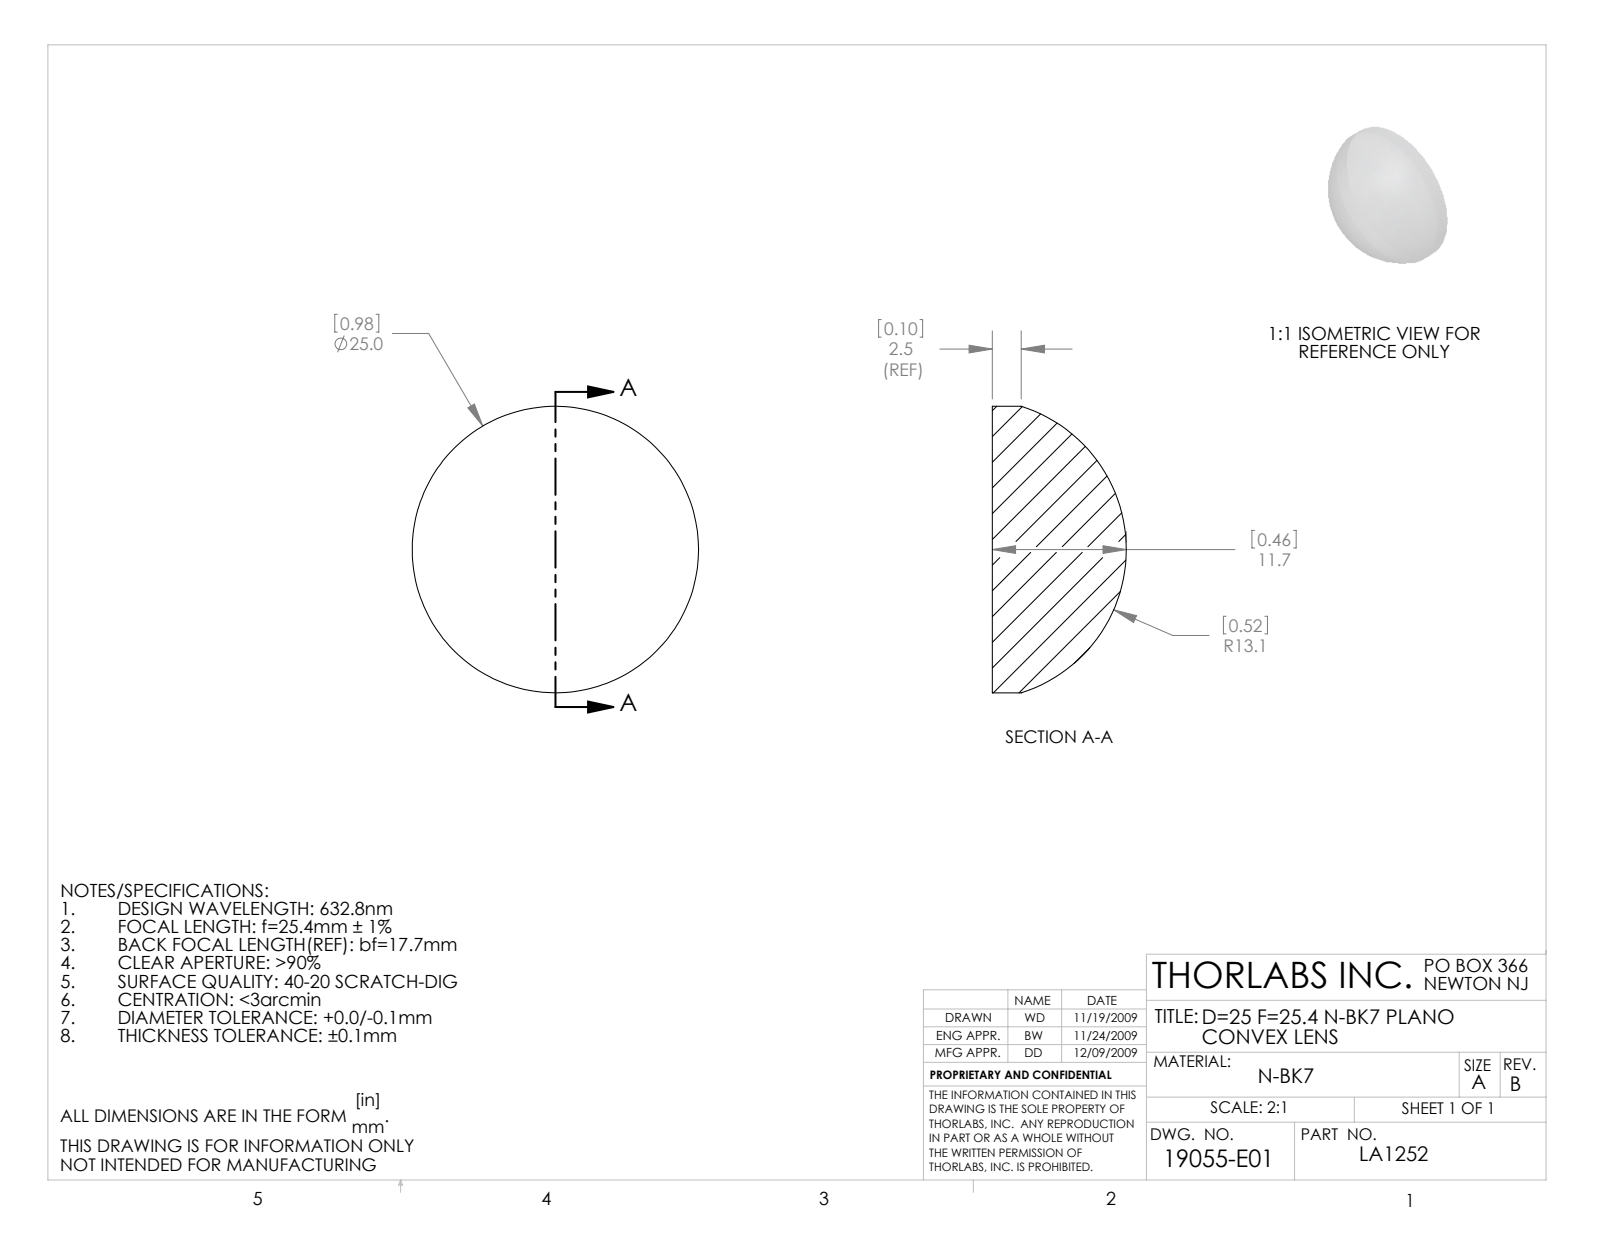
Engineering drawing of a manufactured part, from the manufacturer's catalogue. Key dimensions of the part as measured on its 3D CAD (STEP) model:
Part name (STEP PRODUCT): 19055-E0W
STEP written by: SolidWorks 2009 (AUTOMOTIVE_DESIGN)
Units: millimetres
Bodies: 1 solid, 5 faces (1 planar, 2 cylindrical, 2 other)
Overall size (bounding box): 25 × 25 × 11.7
Volume: 3 895 mm³ · Surface area: 1 444 mm²
Round bosses / shafts (diameter × count): ⌀25 ×1
